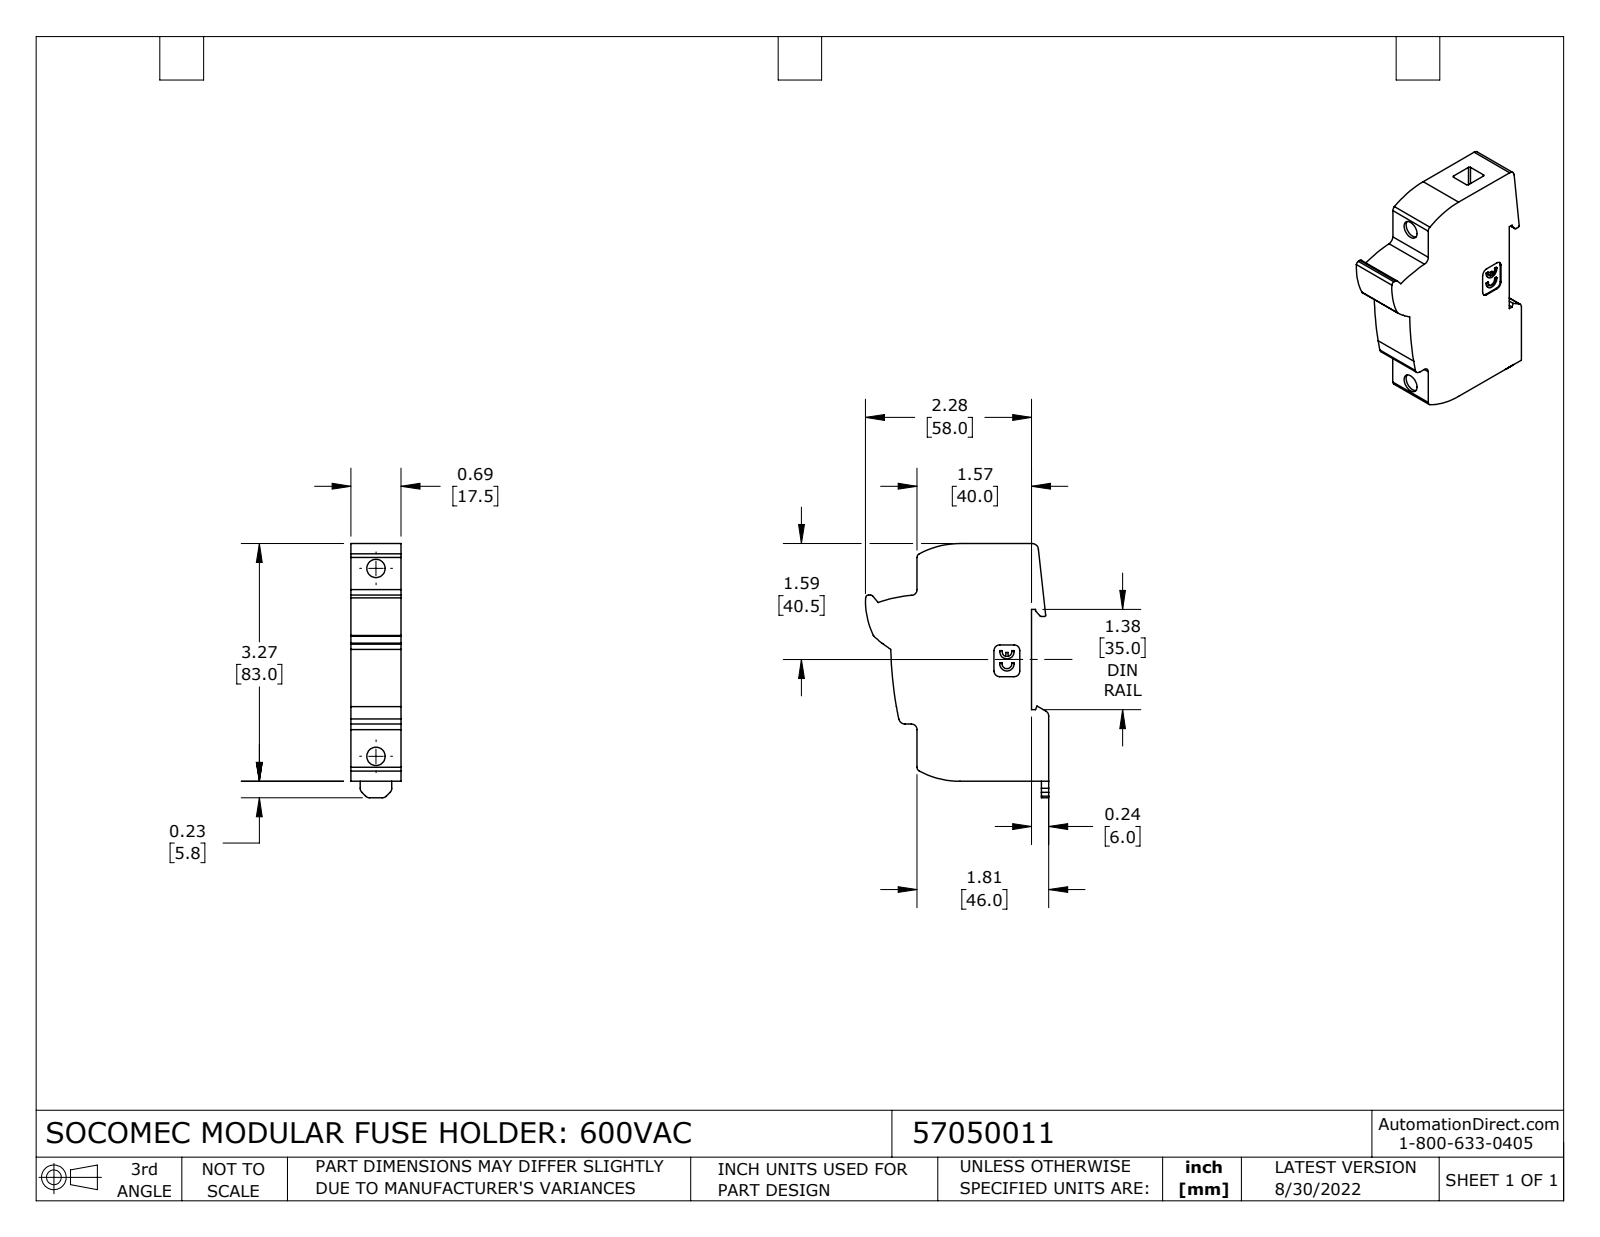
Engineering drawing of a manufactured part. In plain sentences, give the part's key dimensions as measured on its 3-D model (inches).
The part is named "57050011". Its 3-D file was written by "SolidWorks 2021 (CONFIG_CONTROL_DESIGN)". It is 1 solid with 105 faces: 52 planar, 53 cylindrical and 0 other. Overall it measures 3.496 by 2.52 by 0.689 inches. Its volume is 4.229 cubic inches and its surface area 21.33 square inches. Round holes: 2 of diameter 0.252. Partial cylindrical surfaces (rounded edges, fillets, slot ends): 11 of radius 0.079, 5 of radius 0.02, 4 of radius 0.039, 2 of radius 0.059, 2 of radius 0.067, 2 of radius 0.087, 2 of radius 0.098, 2 of radius 1.186. The main face-to-face distances are 0.689, 0.236, 1.575, 3.268, 1.811, 0.199, 0.49, 0.291, 0.518, 0.281. The hole center spacings are 2.583.
